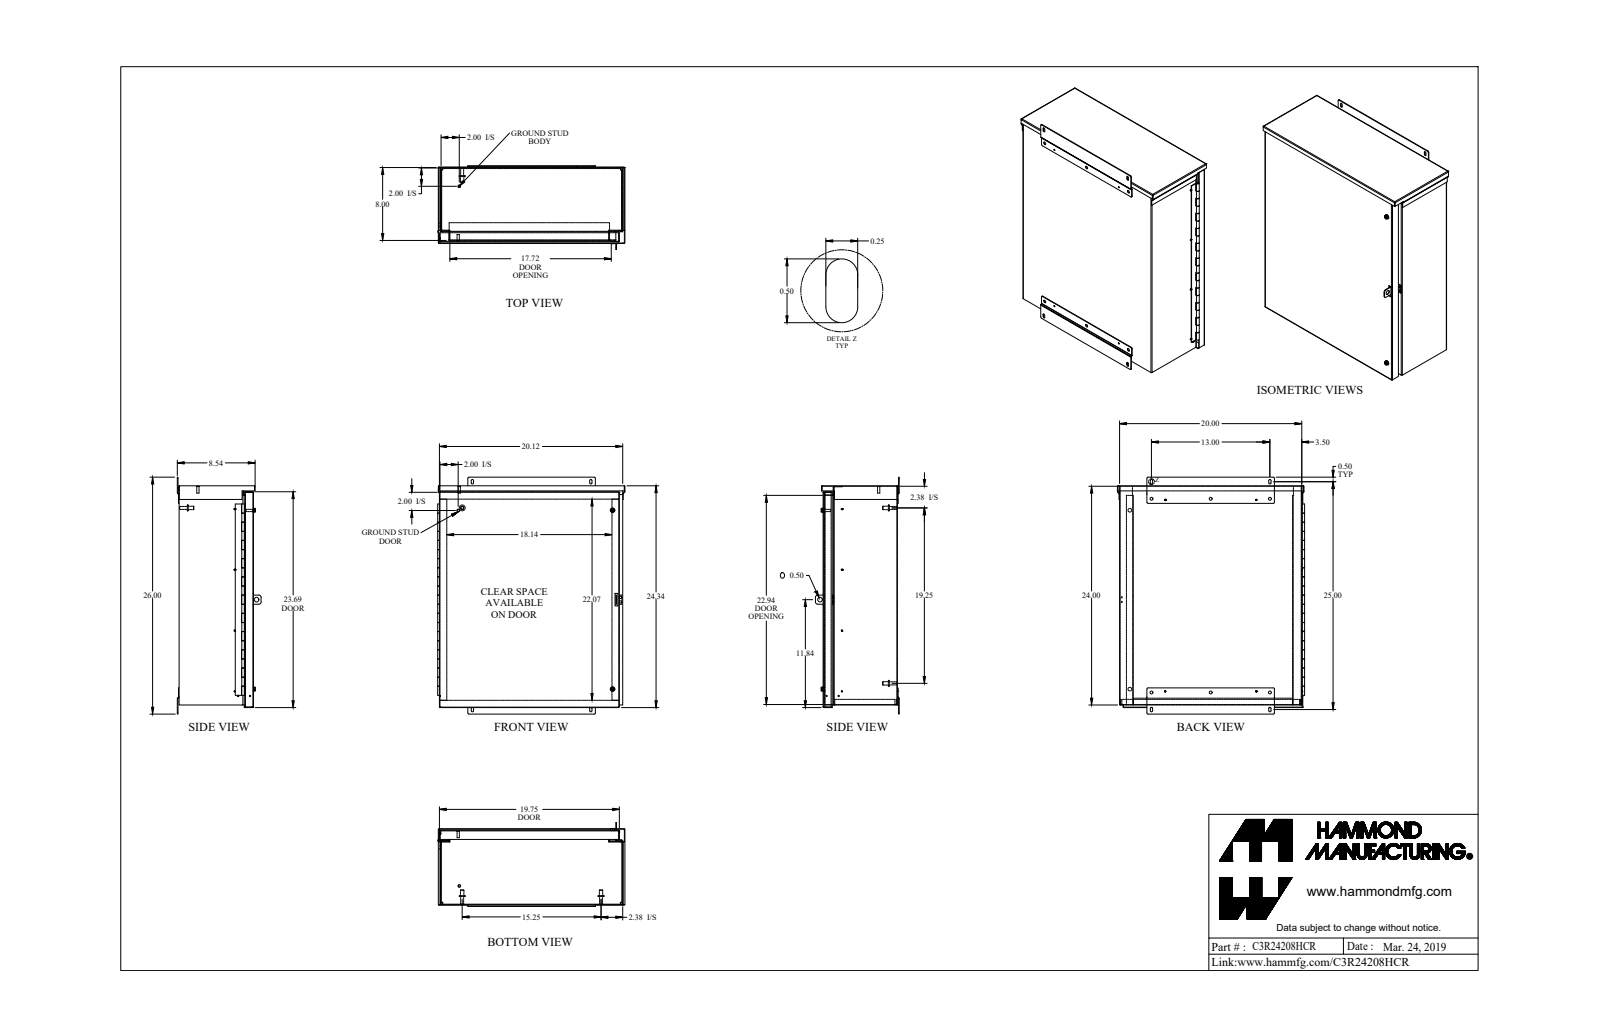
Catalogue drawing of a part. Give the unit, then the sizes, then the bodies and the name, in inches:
Units: inches
Overall size (bounding box): 26 × 20.556 × 9.197
Round holes (diameter × count): ⌀0.313 ×9, ⌀0.14 ×4, ⌀0.26 ×3, ⌀0.137 ×2, ⌀0.266 ×2, ⌀0.28 ×2, ⌀0.29 ×2, ⌀0.397 ×2, ⌀0.188 ×1, ⌀0.5 ×1
Round bosses / shafts (diameter × count): ⌀0.131 ×10, ⌀0.65 ×4, ⌀0.375 ×4, ⌀0.33 ×4, ⌀0.51 ×3, ⌀0.244 ×3, ⌀0.187 ×3, ⌀0.5 ×2
Partial cylindrical surfaces — rounded edges, fillets, slot ends (radius × count): R0.029 ×26, R0.086 ×26, R0.125 ×19, R0.036 ×5, R0.108 ×5, R0.171 ×3, R0.25 ×2
Main face-to-face distances: 0.057, 8.1, 8.043, 8.157, 19.943, 24, 20, 23.943, 19.886, 24.057
Hole centre spacings: 1.505, 5.002, 6.5, 11.501, 21.178, 21.709, 22.222, 24.052
Volume: 131.6 in³ · Surface area: 4 330 in²
Bodies: 33 solids, 888 faces (499 planar, 335 cylindrical, 54 other)
Part name (STEP PRODUCT): C3R24208HCR_Default
STEP written by: SolidWorks 2019 (CONFIG_CONTROL_DESIGN)
